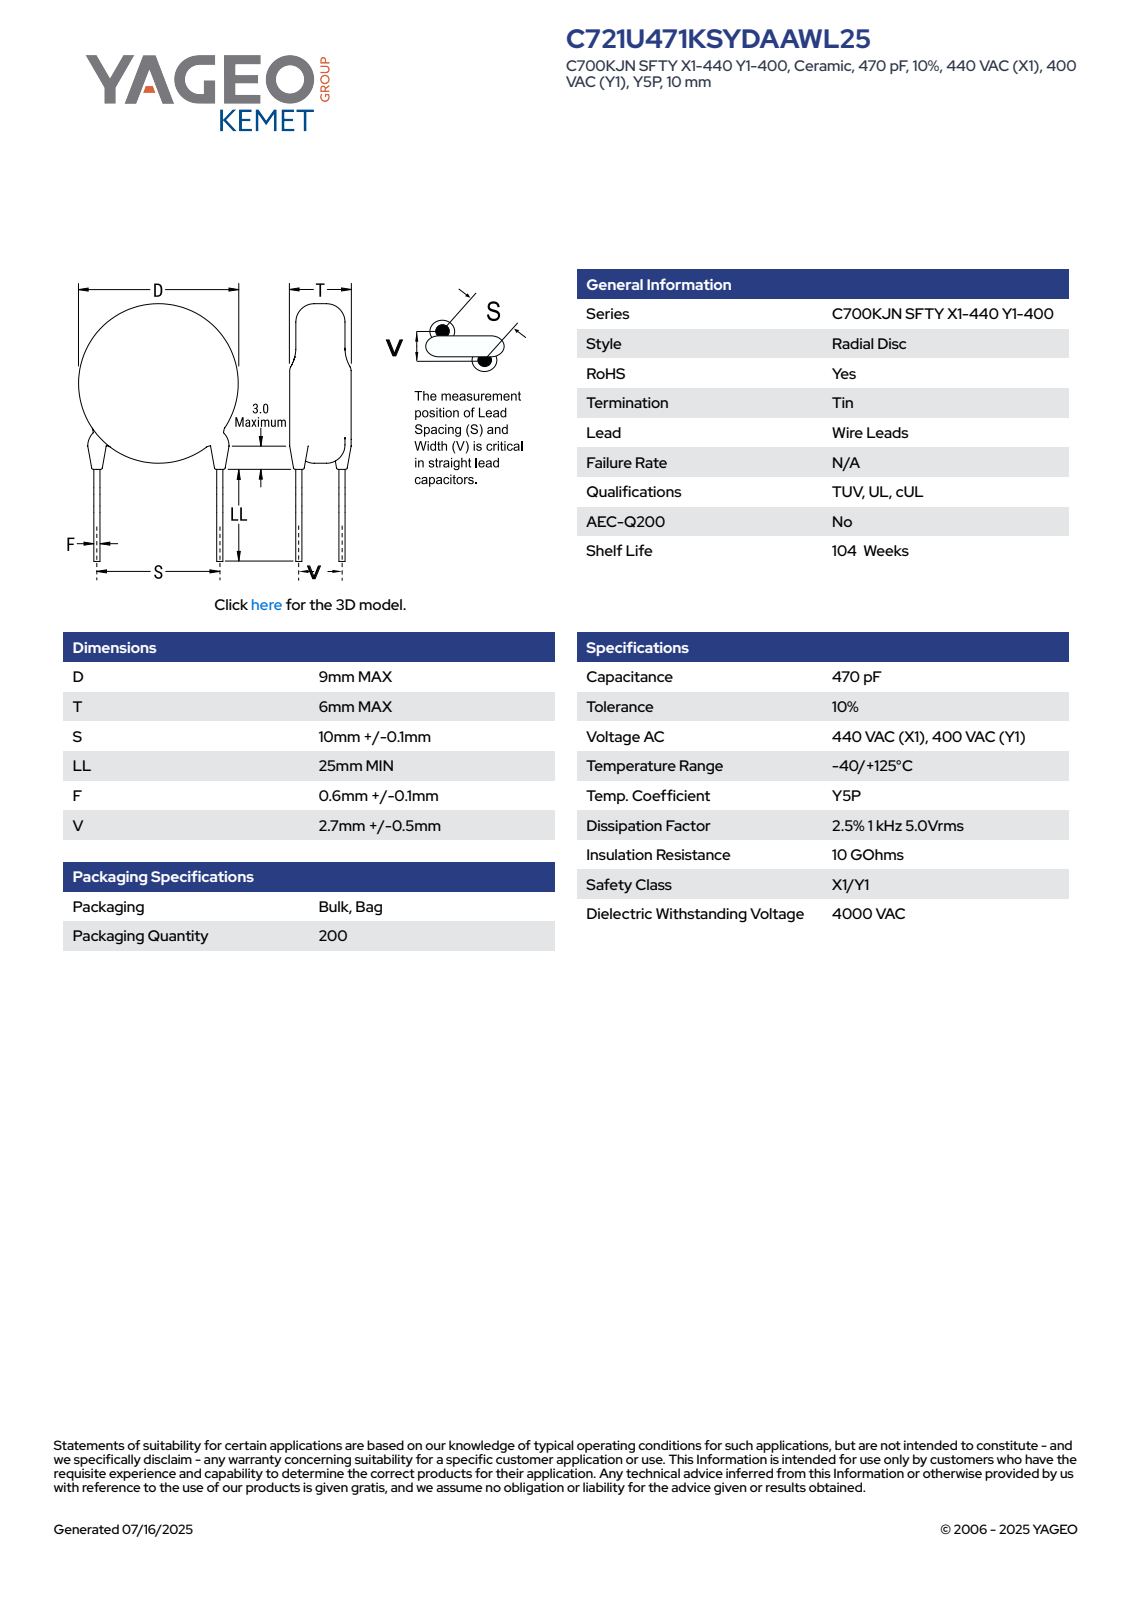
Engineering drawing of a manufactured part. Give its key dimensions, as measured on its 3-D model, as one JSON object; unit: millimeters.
{"part_name": "CCD_KST_9X6_D9T6S10.1LL25F0.7V2.7", "step_written_by": "SolidWorks 2021 (AUTOMOTIVE_DESIGN)", "units": "millimeters", "bodies": {"solids": 4, "faces": 81, "planar": 63, "cylindrical": 14, "other": 4}, "overall_size": [35.31, 11.2, 6], "volume_mm3": 399, "surface_area_mm2": 421, "round_bosses_or_shafts": [[1.2, 4], [0.7, 2], [9, 1]], "face_to_face_distances": [6, 25, 1.07, 31.43, 6.43, 30.36, 5.36, 4.36, 0.4, 0.86]}
